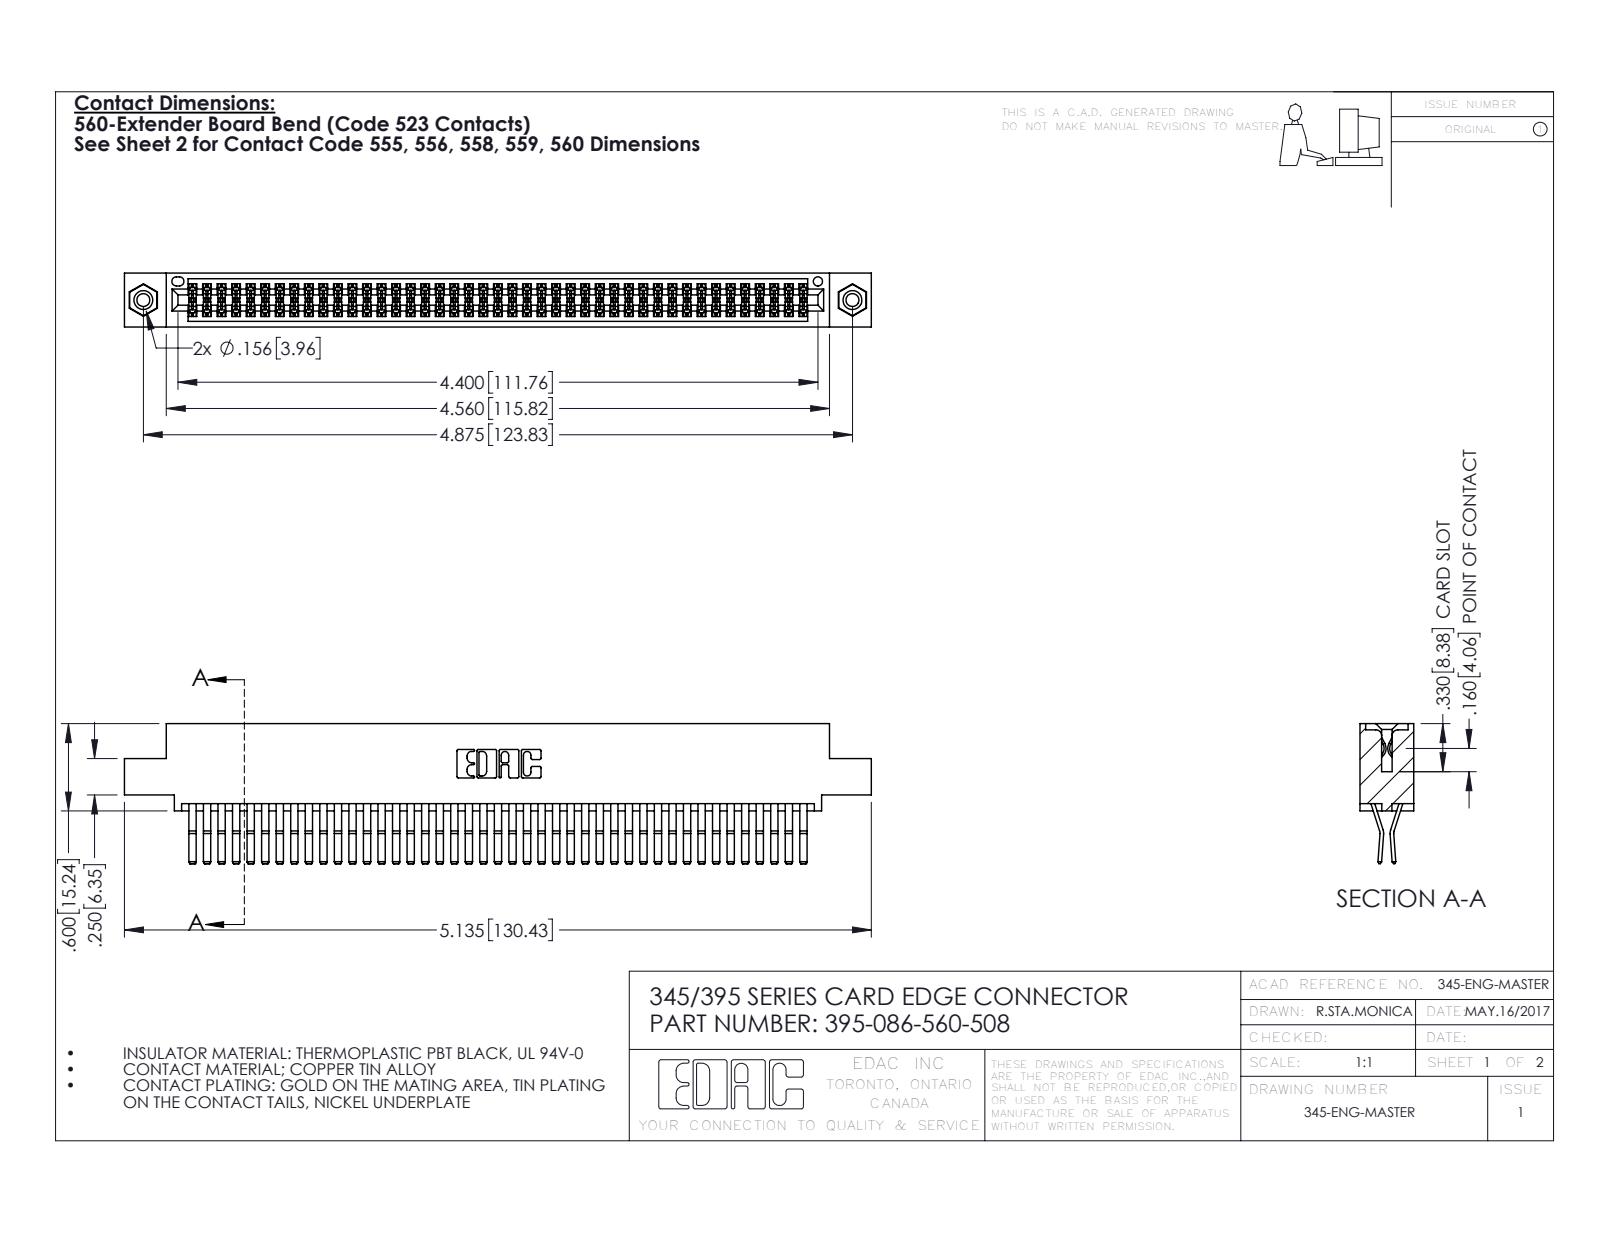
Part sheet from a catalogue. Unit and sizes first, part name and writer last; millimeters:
Units: millimetres
Overall size (bounding box): 130.4 × 24.4 × 9.4
Round holes (diameter × count): ⌀2.3 ×2, ⌀3.2 ×2, ⌀4 ×2, ⌀1.6 ×1
Round bosses / shafts (diameter × count): ⌀3.9 ×2
Partial cylindrical surfaces — rounded edges, fillets, slot ends (radius × count): R0.2 ×130, R0.3 ×22, R0.2 ×6, R0.8 ×6, R0.7 ×3, R0.3 ×2, R0.4 ×2, R0.5 ×2
Main face-to-face distances: 0.6, 1.8, 7.6, 9.4, 5.1, 2.5, 6.9, 5.7, 4.4, 3.8
Hole centre spacings: 6.9, 117.8, 123.8
Volume: 13 200 mm³ · Surface area: 21 030 mm²
Bodies: 89 solids, 4662 faces (2954 planar, 1692 cylindrical, 16 other)
Part name (STEP PRODUCT): 345 Part_0.110 Offset - 0.156 Dia-TI; 345-292-001_560 Tail; 395-086-560-508; 345-250-001_345-250-003-102
STEP written by: SolidWorks 2016 (CONFIG_CONTROL_DESIGN)
